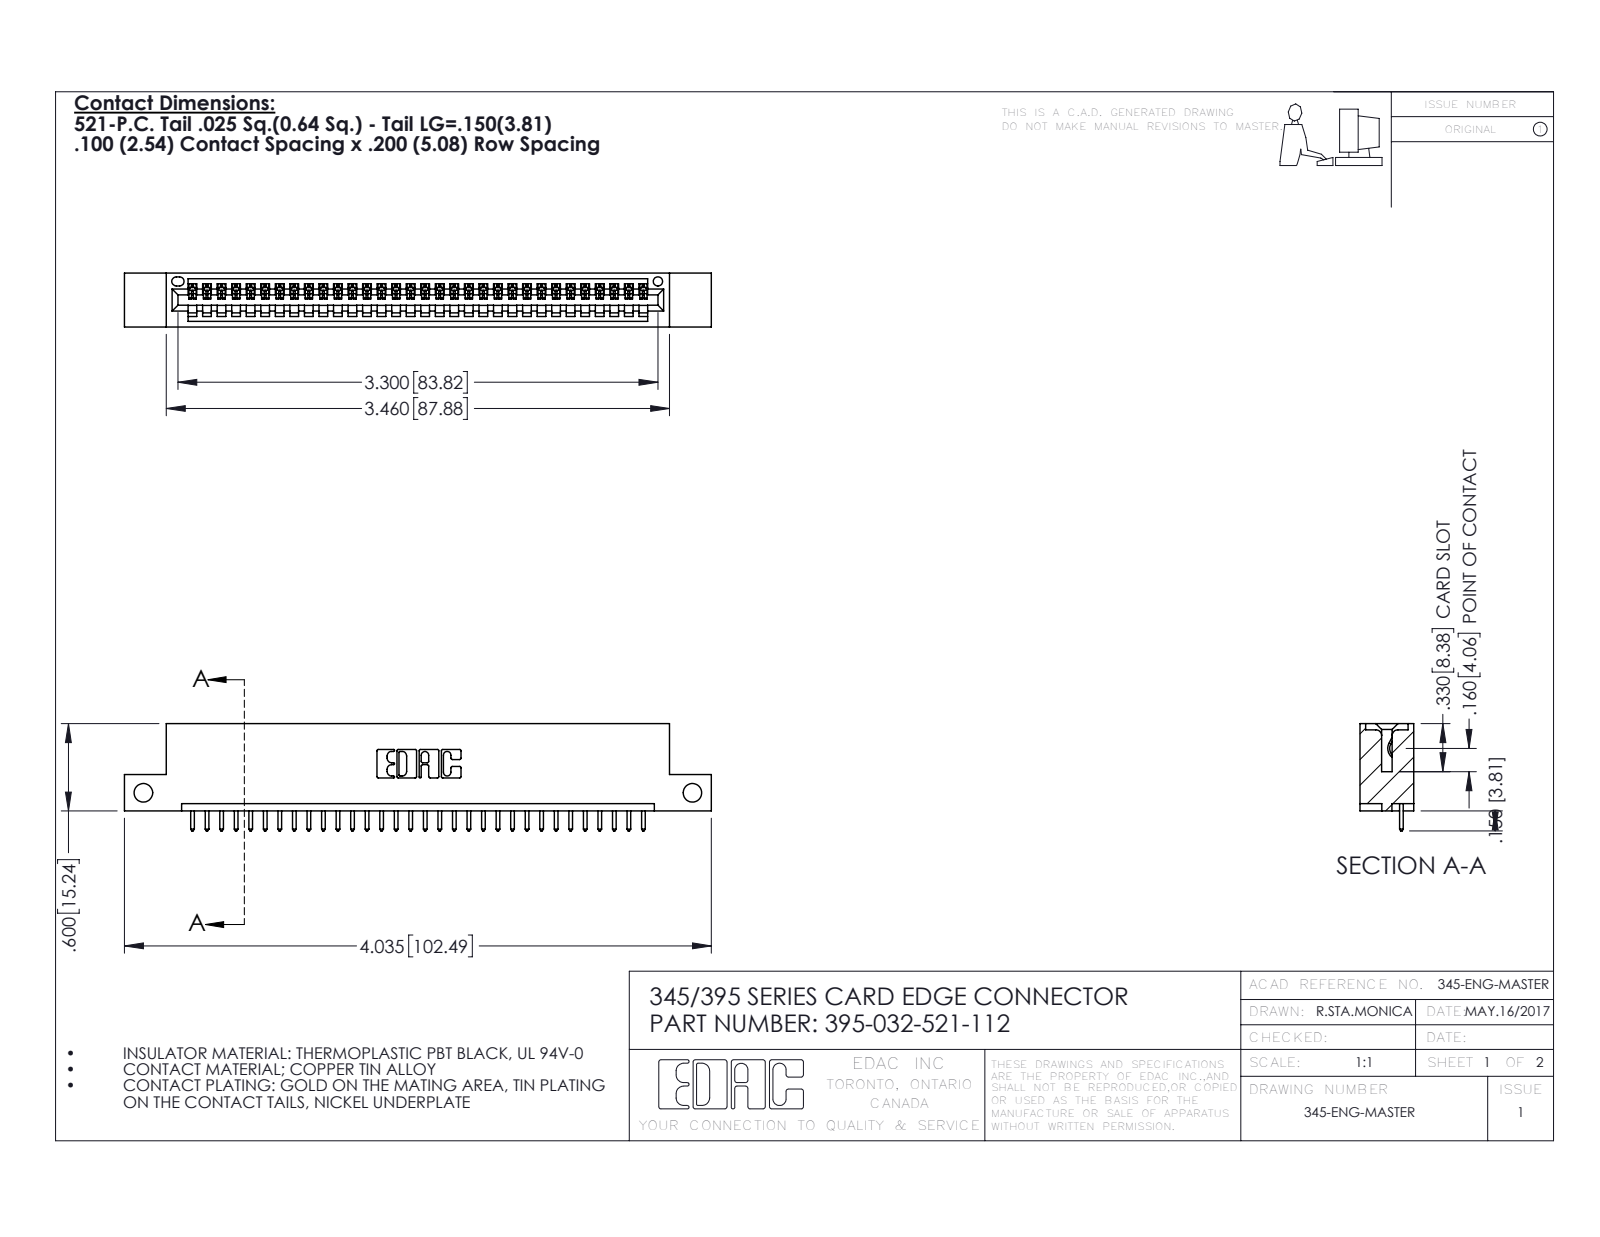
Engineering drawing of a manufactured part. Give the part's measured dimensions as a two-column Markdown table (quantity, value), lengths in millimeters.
| quantity | value |
| --- | --- |
| part name | 345-292-001_345-293-121; 395-032-521-112; 345 Part_Flush Mounting Lugs - Side Mount |
| STEP written by | SolidWorks 2016 (CONFIG_CONTROL_DESIGN) |
| units | millimeters |
| bodies | 33 solids, 1982 faces (1360 planar, 622 cylindrical, 0 other) |
| overall size | 102.5 × 18.7 × 9.4 |
| volume | 9 470 mm³ |
| surface area | 11 950 mm² |
| round holes (diameter × count) | 3.3 × 2, 1.6 × 1 |
| partial cylindrical surfaces (radius × count) | 0.2 × 64, 0.3 × 64, 0.3 × 22, 0.2 × 6, 0.8 × 6, 0.7 × 3, 0.8 × 2, 1 × 2 |
| main face-to-face distances | 7.6, 1.8, 5.1, 9.4, 2.5, 6.9, 0.6, 5.7, 3.8, 1.8 |
| hole center spacings | 95.9 |
